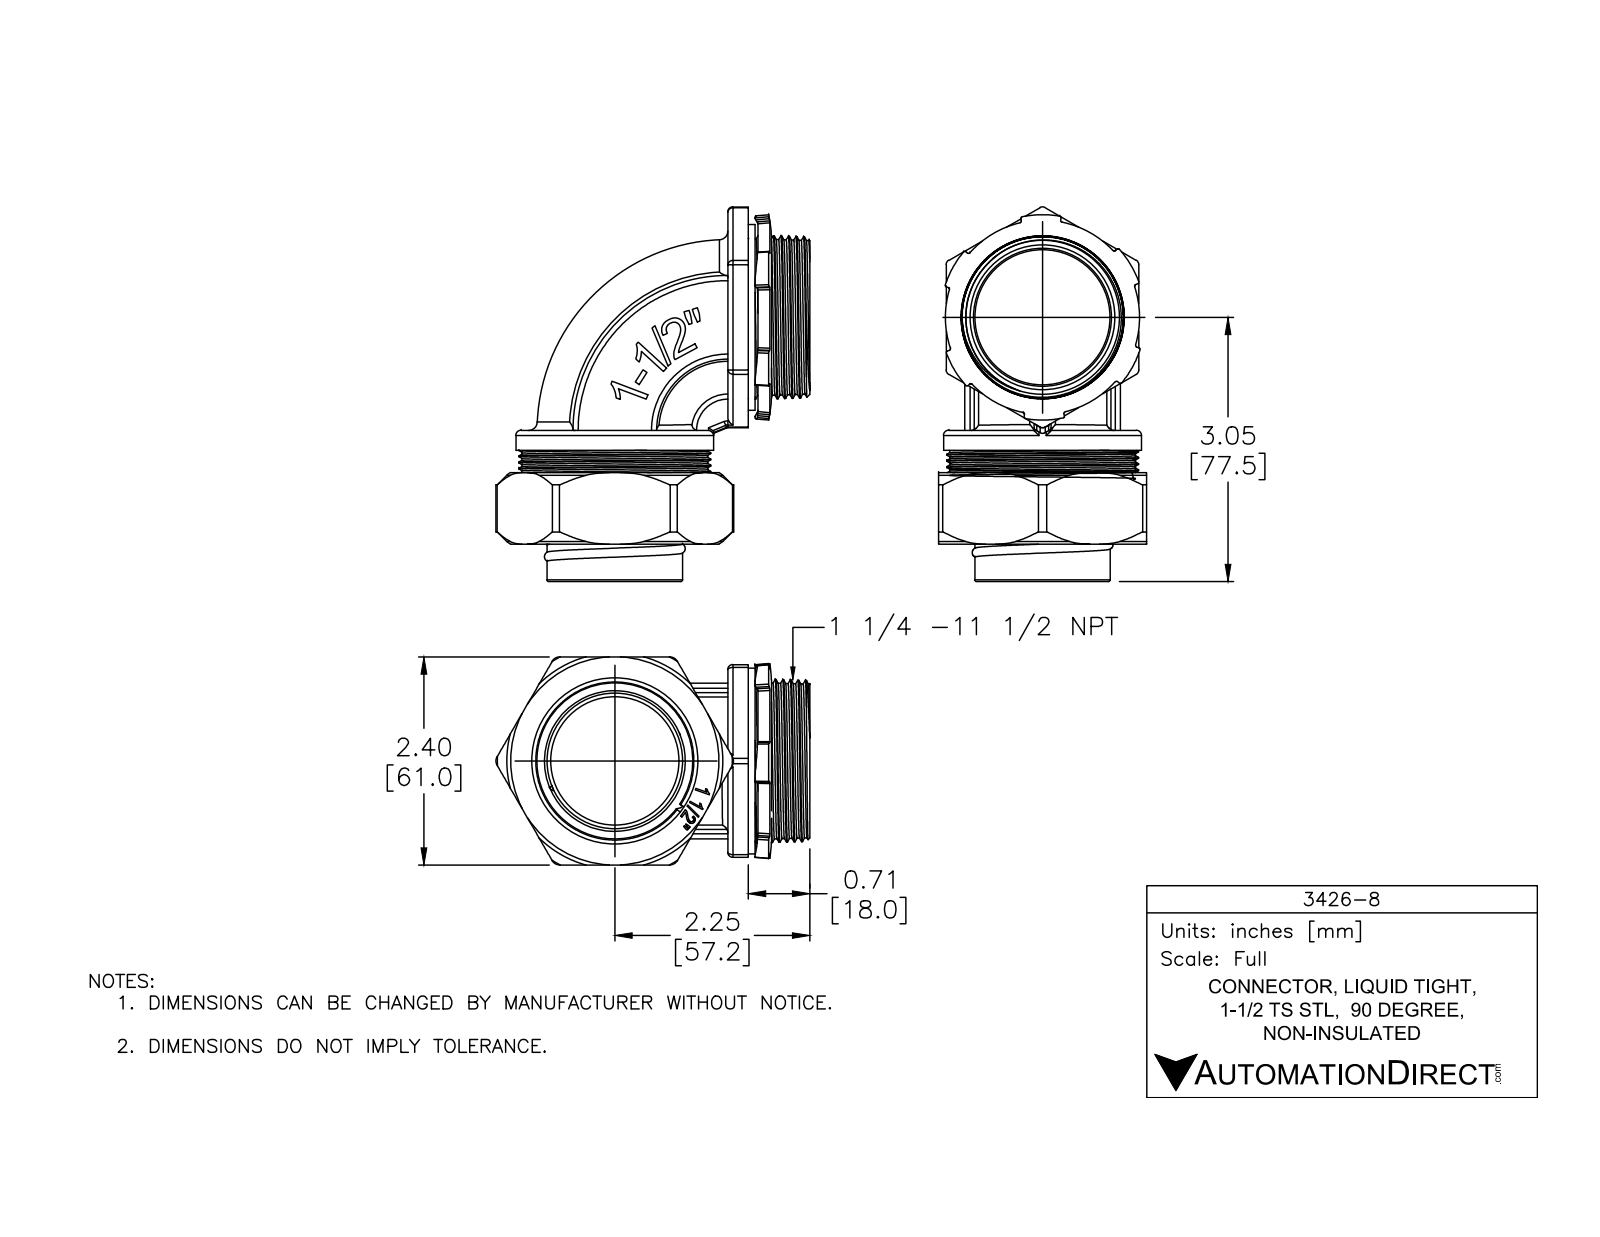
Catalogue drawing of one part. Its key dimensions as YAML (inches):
part_name: "3426-8"
step_written_by: "SolidWorks 2018 (AUTOMOTIVE_DESIGN)"
units: inches
bodies: {solids: 6, faces: 658, planar: 263, cylindrical: 140, other: 255}
overall_size: [4.323, 3.622, 2.402]
volume: 5.023
surface_area: 111.1
round_holes:
  - {diameter: 0.192, count: 1}
  - {diameter: 1.482, count: 1}
  - {diameter: 1.524, count: 1}
  - {diameter: 1.56, count: 1}
  - {diameter: 1.575, count: 1}
  - {diameter: 1.592, count: 1}
  - {diameter: 1.795, count: 1}
  - {diameter: 1.878, count: 1}
  - {diameter: 1.917, count: 1}
  - {diameter: 1.93, count: 1}
  - {diameter: 1.996, count: 1}
  - {diameter: 2.165, count: 1}
round_bosses_or_shafts:
  - {diameter: 2.283, count: 1}
  - {diameter: 2.213, count: 1}
  - {diameter: 2.146, count: 1}
  - {diameter: 2.098, count: 1}
  - {diameter: 1.969, count: 1}
  - {diameter: 1.563, count: 1}
  - {diameter: 1.522, count: 1}
  - {diameter: 0.156, count: 1}
partial_cylinders:
  - {radius: 0.059, count: 19}
  - {radius: 0.012, count: 8}
  - {radius: 0.094, count: 6}
  - {radius: 0.004, count: 2}
  - {radius: 0.052, count: 2}
  - {radius: 0.006, count: 1}
  - {radius: 0.016, count: 1}
  - {radius: 0.024, count: 1}
face_to_face_distances: [2.402, 0.304, 2.098, 1.795, 1.084, 0.236, 0.315, 0.079, 1.313, 0.229]
hole_center_spacings: [1.085]
